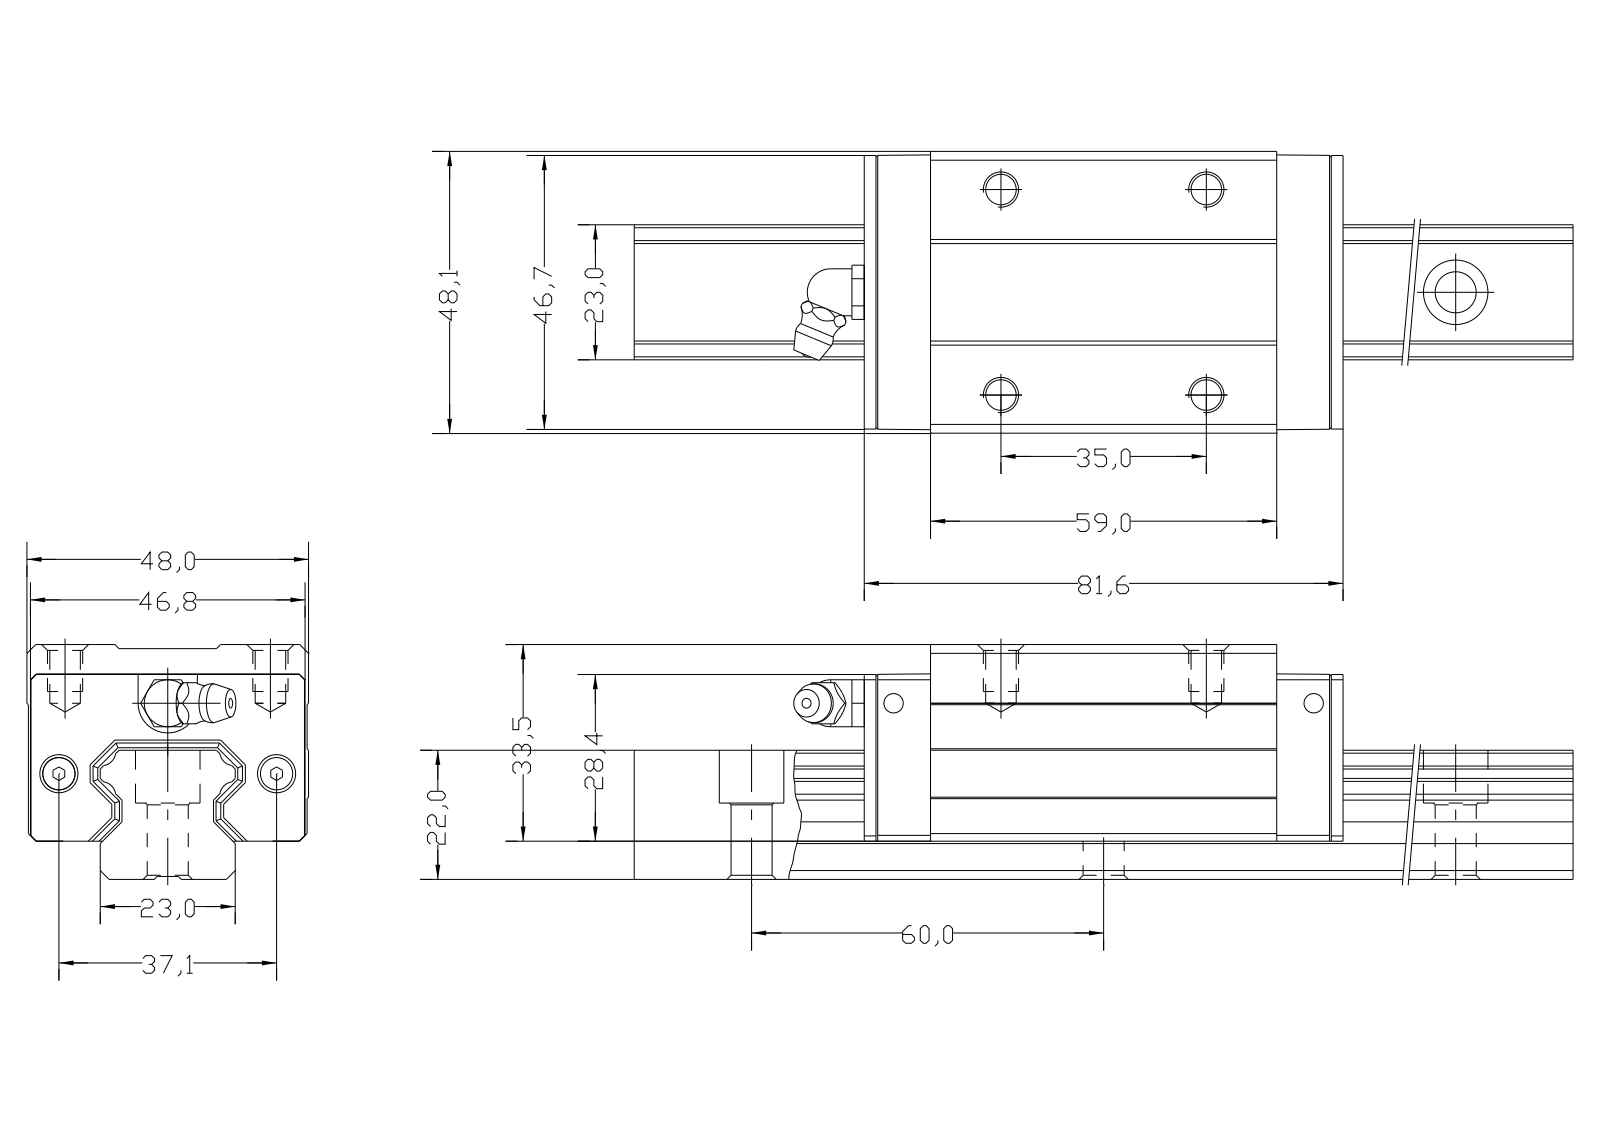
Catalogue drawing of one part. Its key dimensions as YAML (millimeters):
step_written_by: "Kubotek KeyCreator V6.5.2 (0407) (CONFIG_CONTROL_DESIGN)"
units: millimeters
bodies: {solids: 3, faces: 206, planar: 135, cylindrical: 54, other: 17}
overall_size: [220, 48, 40]
volume: 187898
surface_area: 43111
round_holes:
  - {diameter: 6, count: 4}
  - {diameter: 7, count: 4}
  - {diameter: 11, count: 4}
  - {diameter: 3.25, count: 2}
  - {diameter: 6.5, count: 2}
round_bosses_or_shafts:
  - {diameter: 8, count: 1}
partial_cylinders:
  - {radius: 2.65, count: 4}
  - {radius: 5.05, count: 1}
face_to_face_distances: [22, 6.5, 0.7, 3.77, 19.23, 16.02, 31.48, 15.5, 12.25, 35.25]
hole_center_spacings: [21.51, 35, 50.62, 74.58, 108.92, 60, 49.5, 120]
